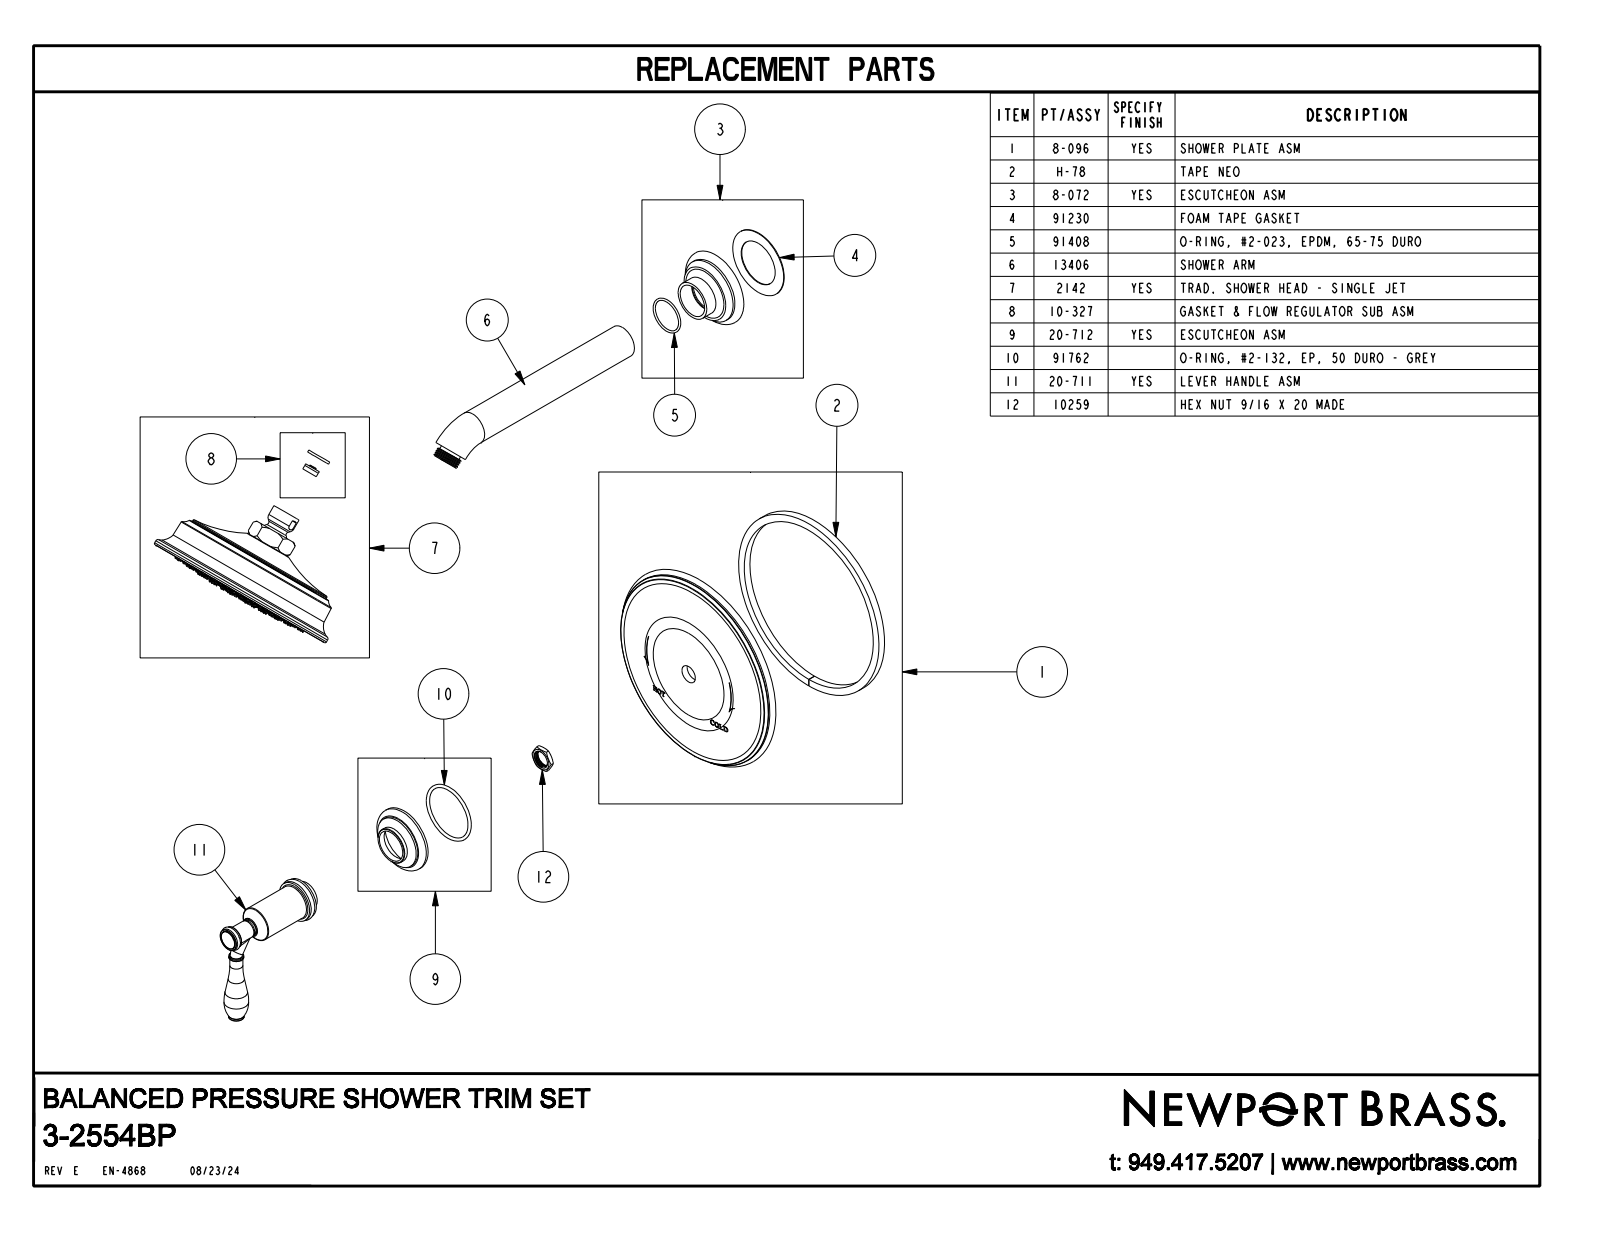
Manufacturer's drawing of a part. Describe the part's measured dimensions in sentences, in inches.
The part is named "3-2554BP". Its 3-D file was written by "CREO PARAMETRIC BY PTC INC, 2018400 (CONFIG_CONTROL_DESIGN)". It is 2 solids with 1102 faces: 241 planar, 238 cylindrical and 623 other. Overall it measures 16.625 by 11.423 by 6.75 inches. Its volume is 62.62 cubic inches and its surface area 223.1 square inches. Round holes: 90 of diameter 0.05, 1 of diameter 0.22, 1 of diameter 0.604, 1 of diameter 5.275. Round bosses or shafts: 2 of diameter 2.11, 2 of diameter 0.6, 1 of diameter 6.51, 1 of diameter 6.2, 1 of diameter 5.22, 1 of diameter 4.83, 1 of diameter 1.7, 1 of diameter 1.42. The main face-to-face distances are 0.48, 0.313, 0.167, 1.015, 1.011, 2.026, 0.47, 0.157, 1.02, 0.707. The hole center spacings are 0.48, 1.84, 2.27, 1.84, 0.952, 3.648, 1.403, 3.187.
